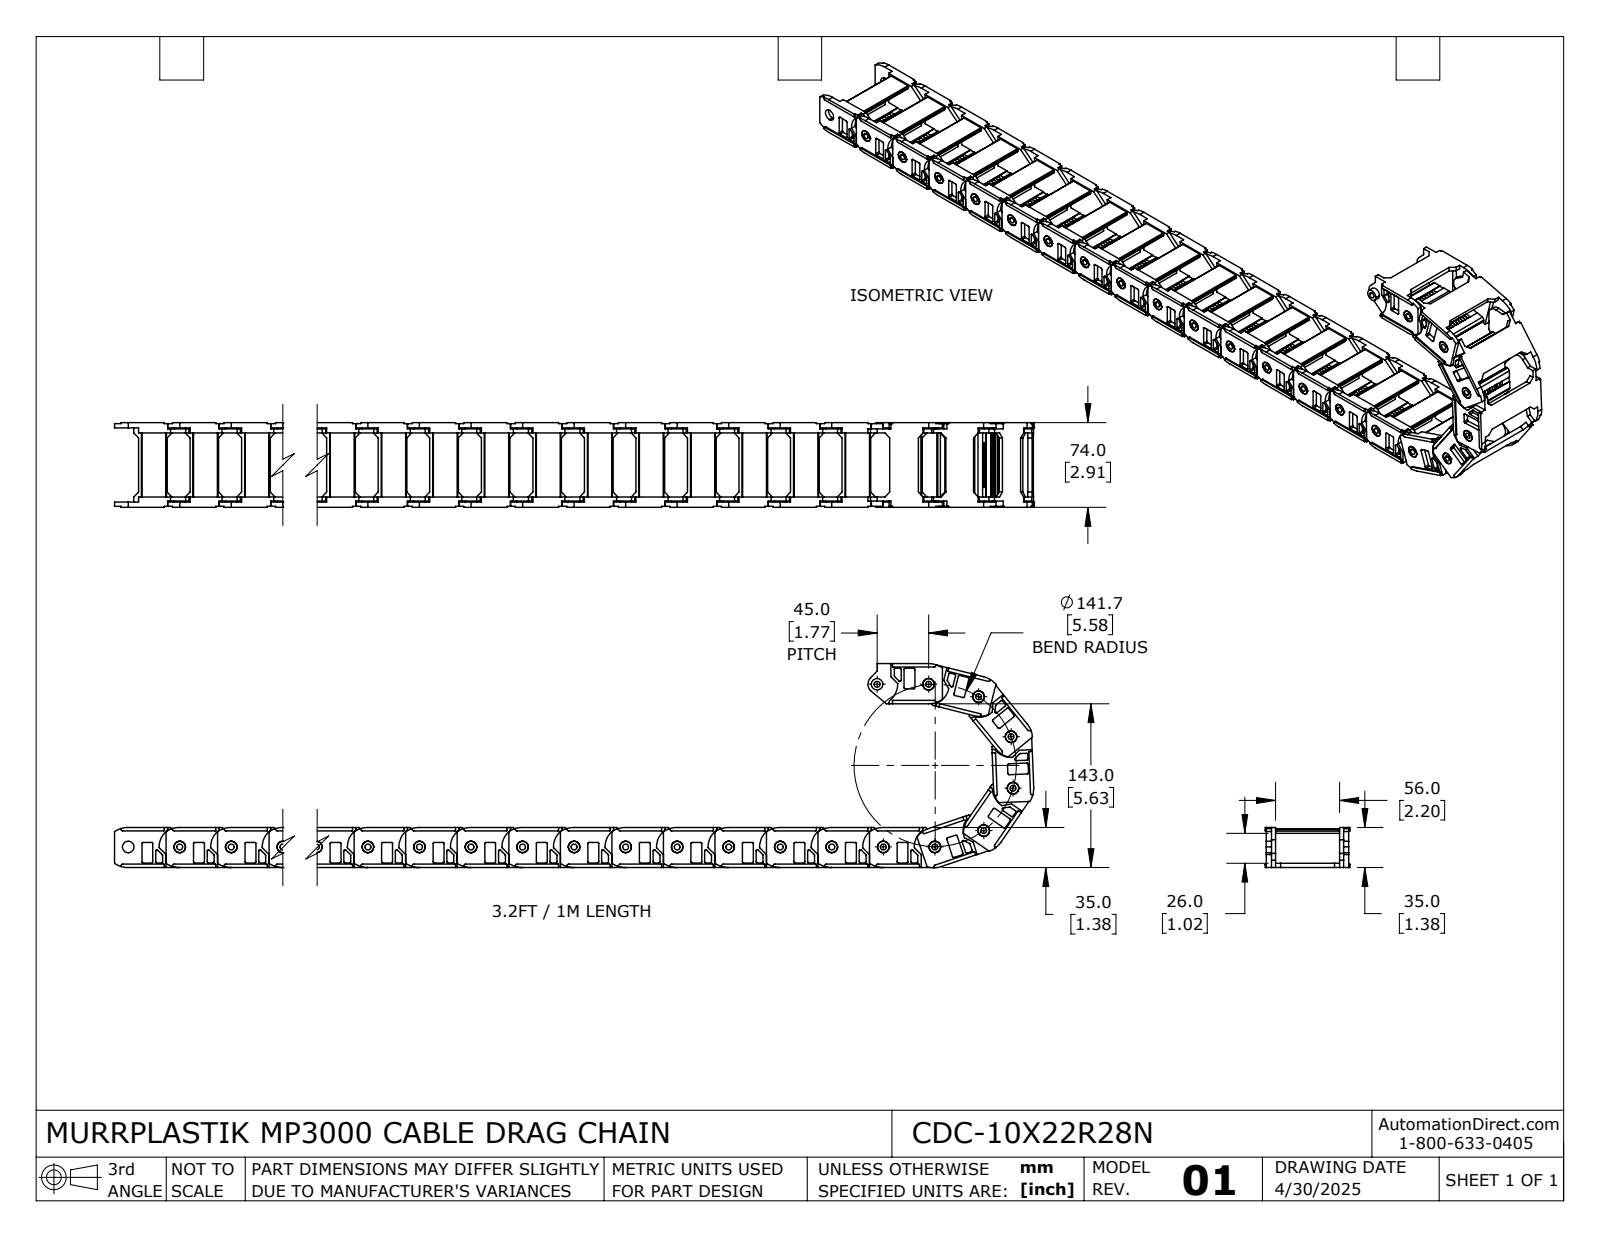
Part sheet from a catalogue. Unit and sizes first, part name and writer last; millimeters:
Units: millimetres
Overall size (bounding box): 818.28 × 178.14 × 74
Round holes (diameter × count): ⌀5.1 ×22, ⌀10.1 ×22
Round bosses / shafts (diameter × count): ⌀10 ×22
Partial cylindrical surfaces — rounded edges, fillets, slot ends (radius × count): R1 ×176, R0.5 ×88, R1.5 ×44, R2 ×44, R21 ×44, R2.8 ×22, R8 ×22, R18 ×22
Main face-to-face distances: 64, 8, 4, 3.7, 68.3, 4.3, 60.3, 56, 3.5, 0.8
Hole centre spacings: 45, 90, 135, 180, 225, 270, 315, 360
Volume: 657 728 mm³ · Surface area: 397 693 mm²
Bodies: 22 solids, 4224 faces (3124 planar, 1100 cylindrical, 0 other)
Part name (STEP PRODUCT): CDC-10X22R28N
STEP written by: SolidWorks 2024 (AUTOMOTIVE_DESIGN)
